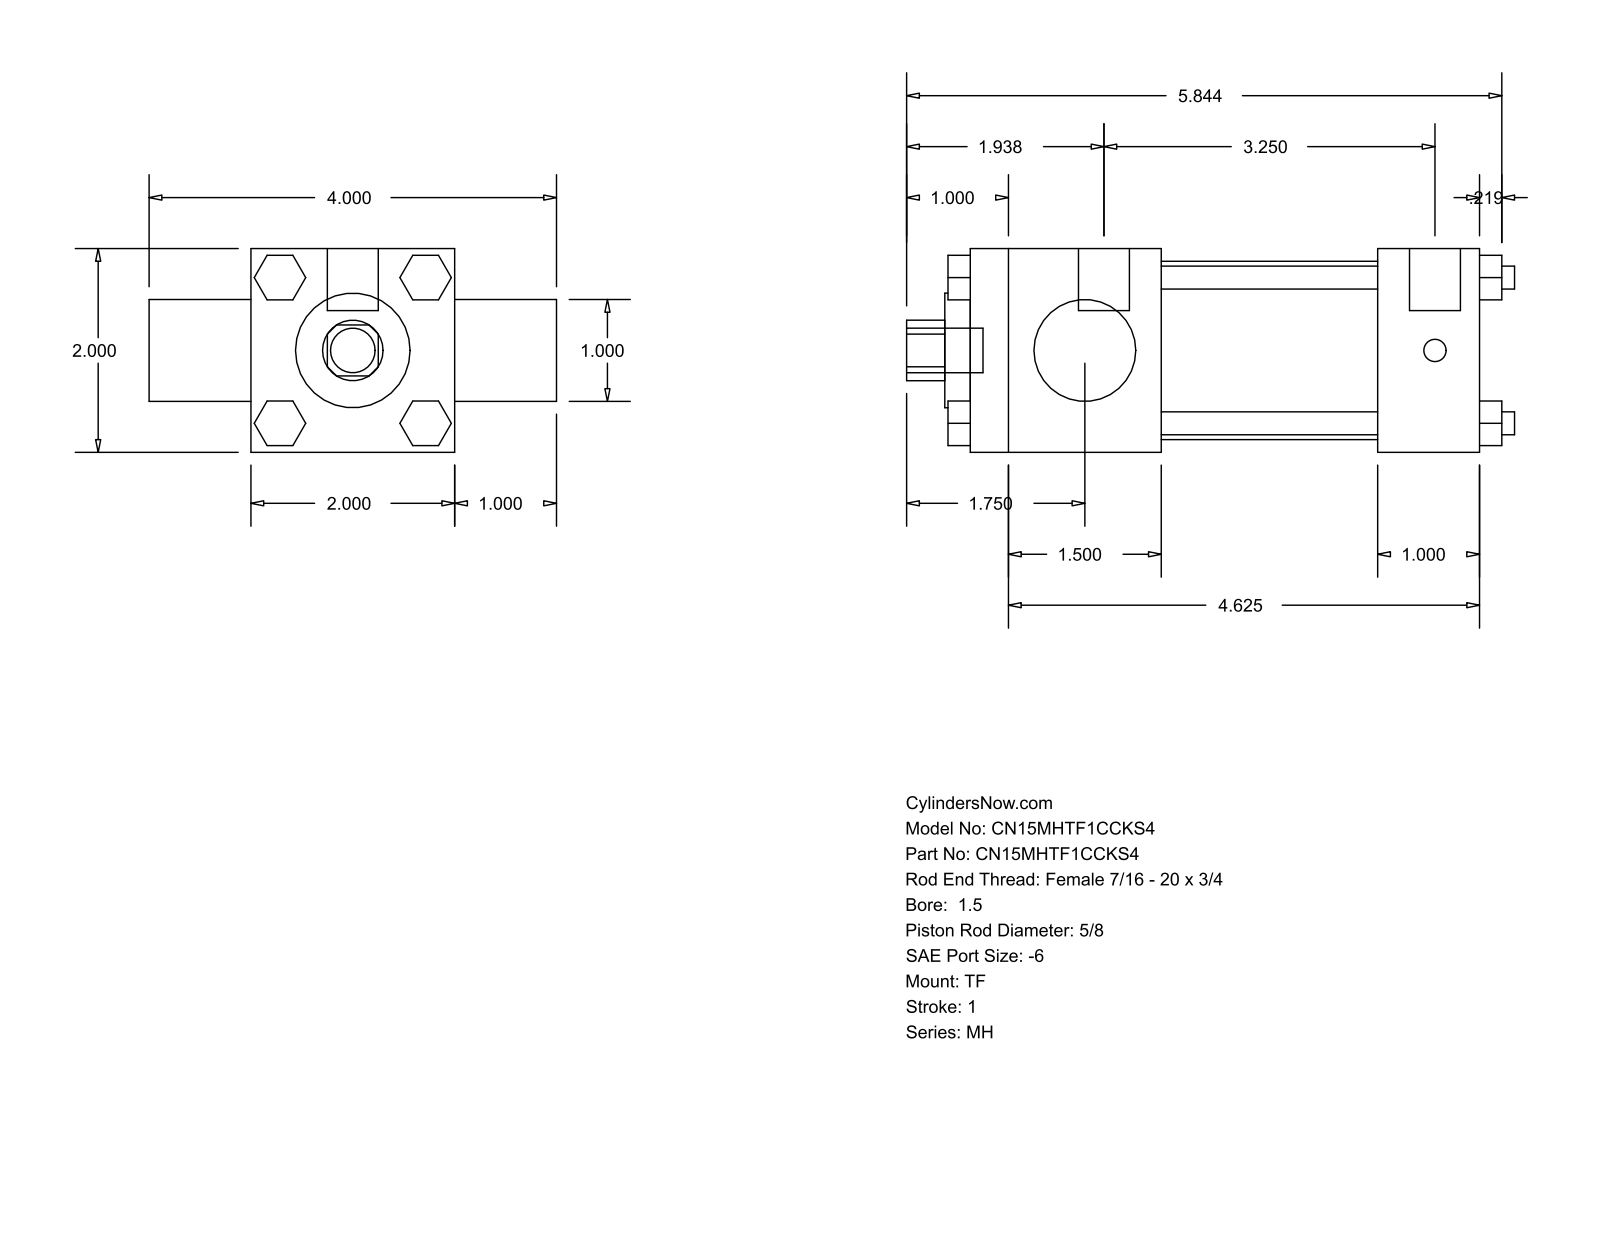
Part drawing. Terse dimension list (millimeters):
name: MH_TF__0150_0.625
written by: GSSL Pune (CONFIG_CONTROL_DESIGN)
unit: mm
bodies: 0 solids, 120 faces (92 planar, 28 cylindrical, 0 other)
size: 151.61 × 101.6 × 50.8
holes: 1× ⌀15.88, 1× ⌀25.4, 1× ⌀28.57, 1× ⌀44.45
bosses: 4× ⌀5.71, 3× ⌀5.56, 2× ⌀12.7, 1× ⌀11.11
rounds: 1× R7.54
face distances: 50.8, 127, 53.97, 25.4, 76.2, 47.62, 79.38, 101.59, 25.41, 11.11
